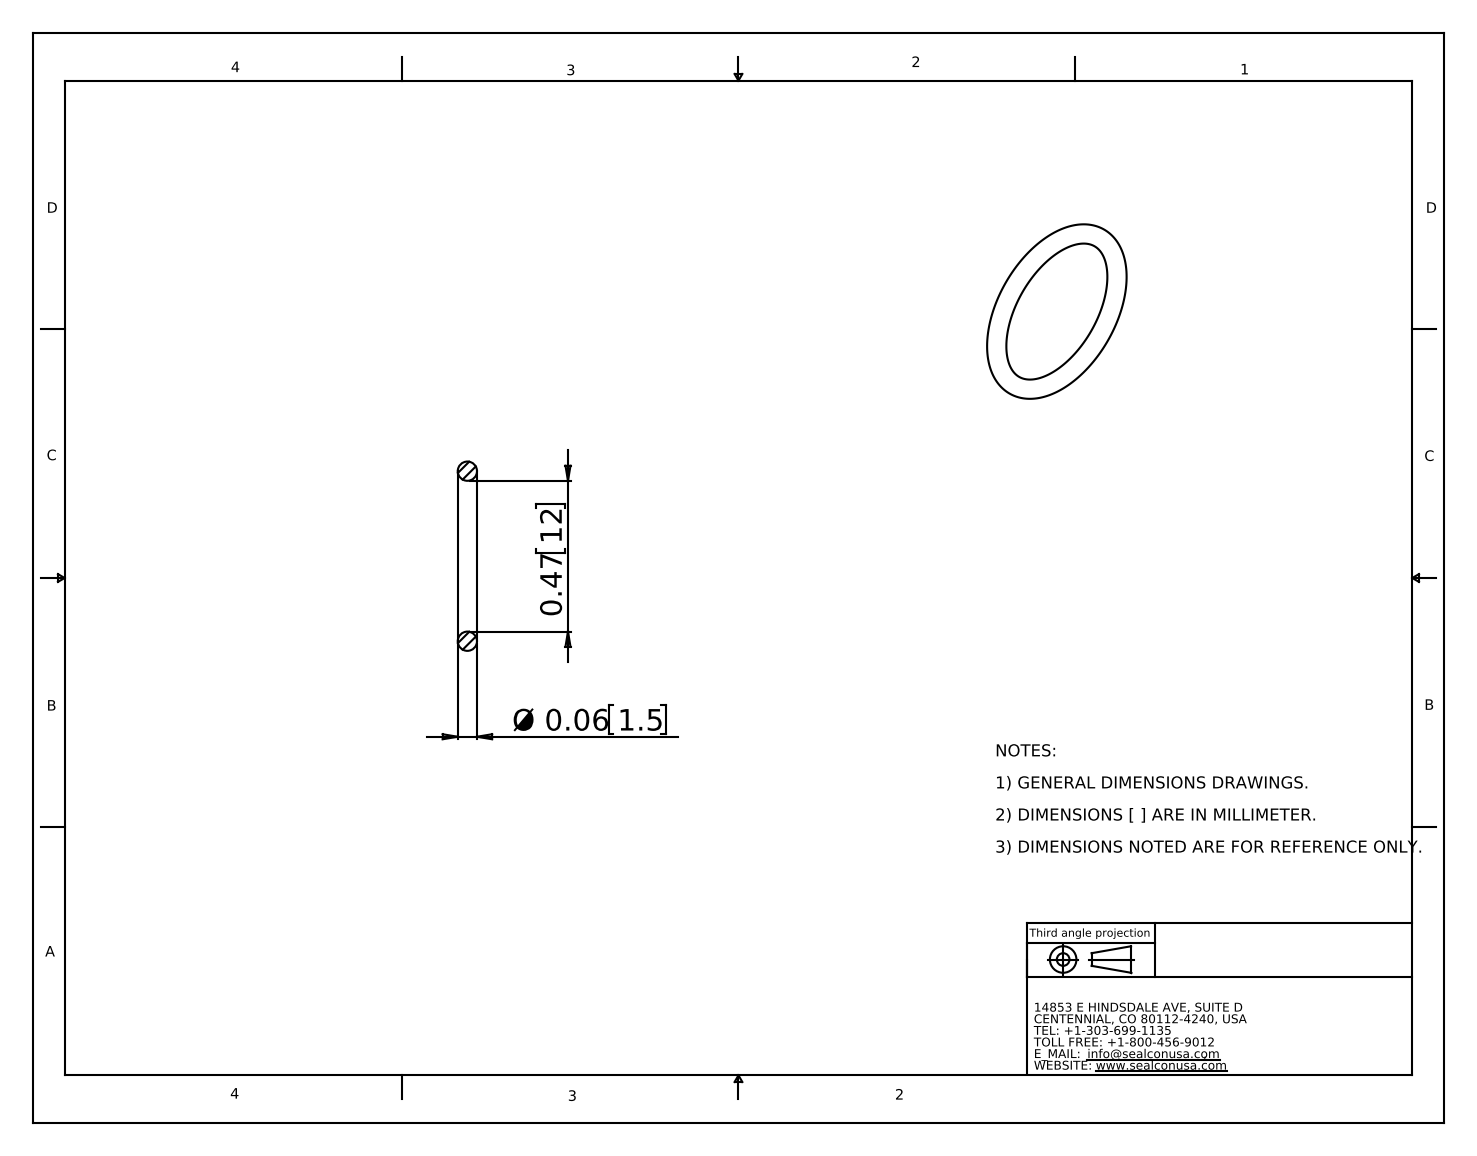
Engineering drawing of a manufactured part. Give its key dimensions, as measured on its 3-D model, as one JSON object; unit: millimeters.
{"part_name": "OM-16-SI", "step_written_by": "SolidWorks 2008 (CONFIG_CONTROL_DESIGN)", "units": "millimeters", "bodies": {"solids": 1, "faces": 4, "planar": 0, "cylindrical": 0, "other": 4}, "overall_size": [15, 15, 1.5], "volume_mm3": 80, "surface_area_mm2": 203}
